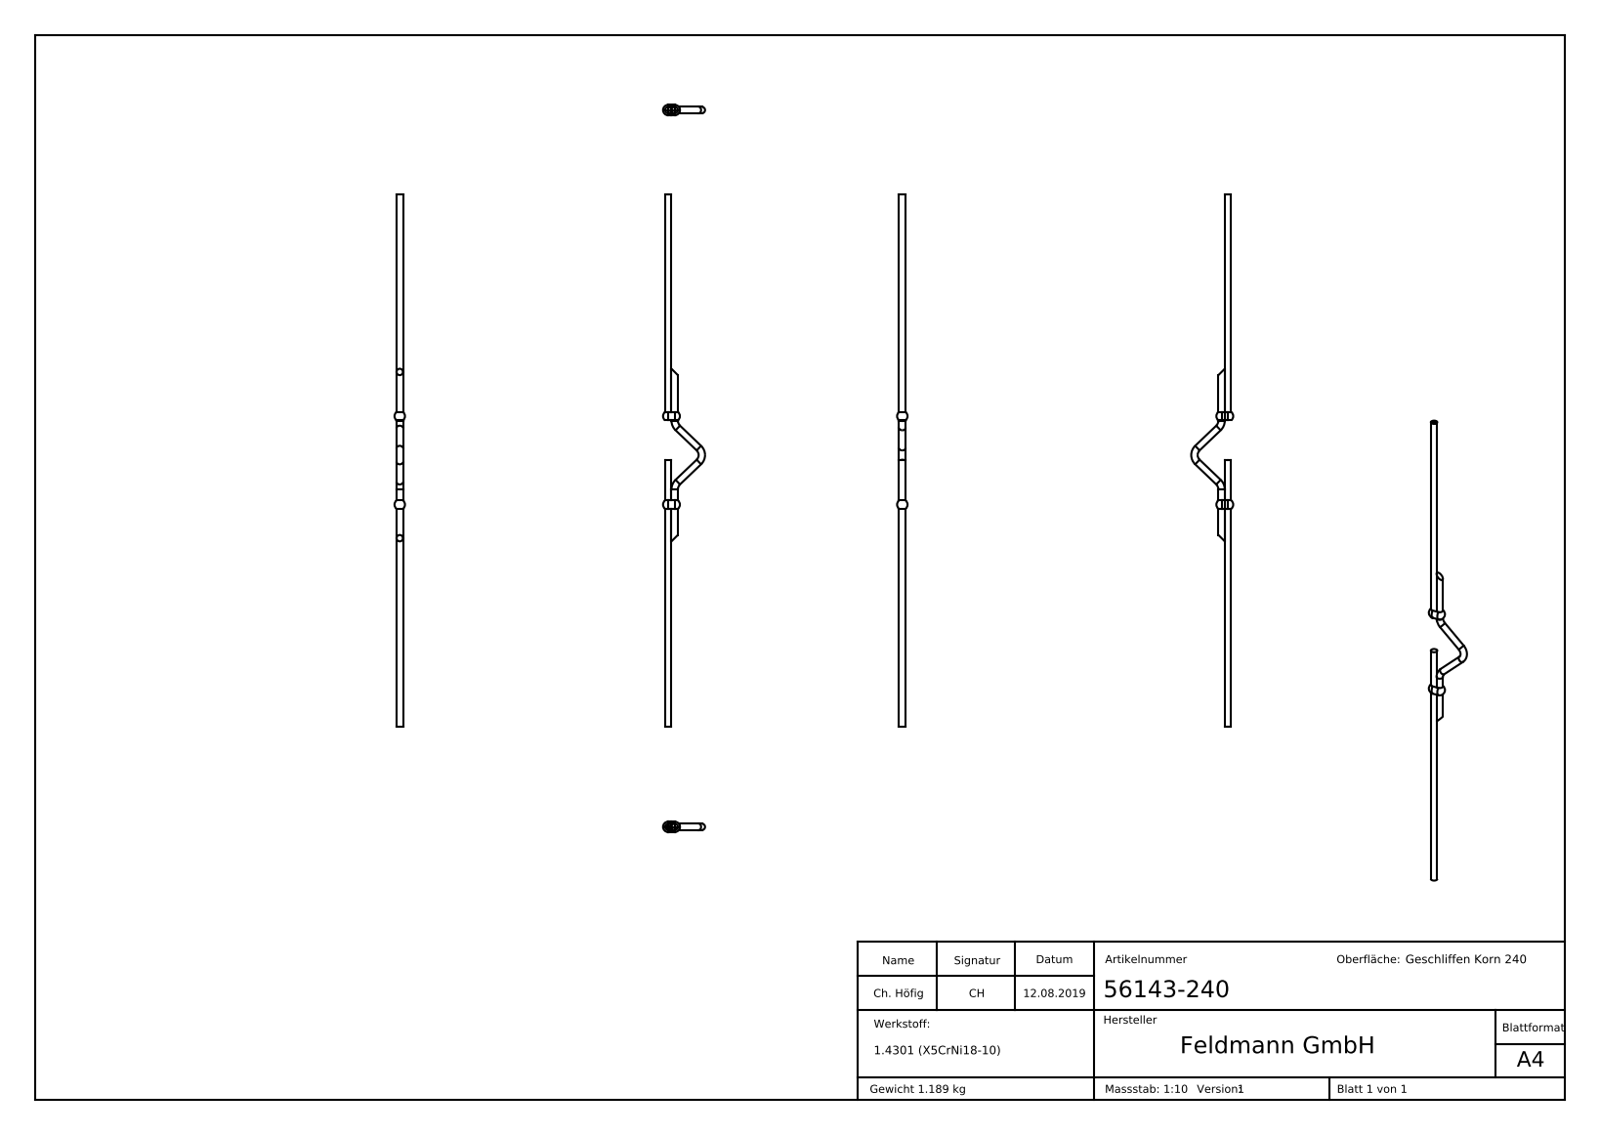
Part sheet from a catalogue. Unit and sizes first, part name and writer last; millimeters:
Units: millimetres
Overall size (bounding box): 1000 × 75 × 19.6
Round bosses / shafts (diameter × count): ⌀12 ×4
Partial cylindrical surfaces — rounded edges, fillets, slot ends (radius × count): R10.32 ×4
Main face-to-face distances: 12, 500, 75, 575, 1000, 425, 999.9, 499.9, 424.9, 2.2
Volume: 150 485 mm³ · Surface area: 53 733 mm²
Bodies: 5 solids, 274 faces (144 planar, 24 cylindrical, 106 other)
Part name (STEP PRODUCT): 56143-240
STEP written by: SolidWorks 2015 (CONFIG_CONTROL_DESIGN)
